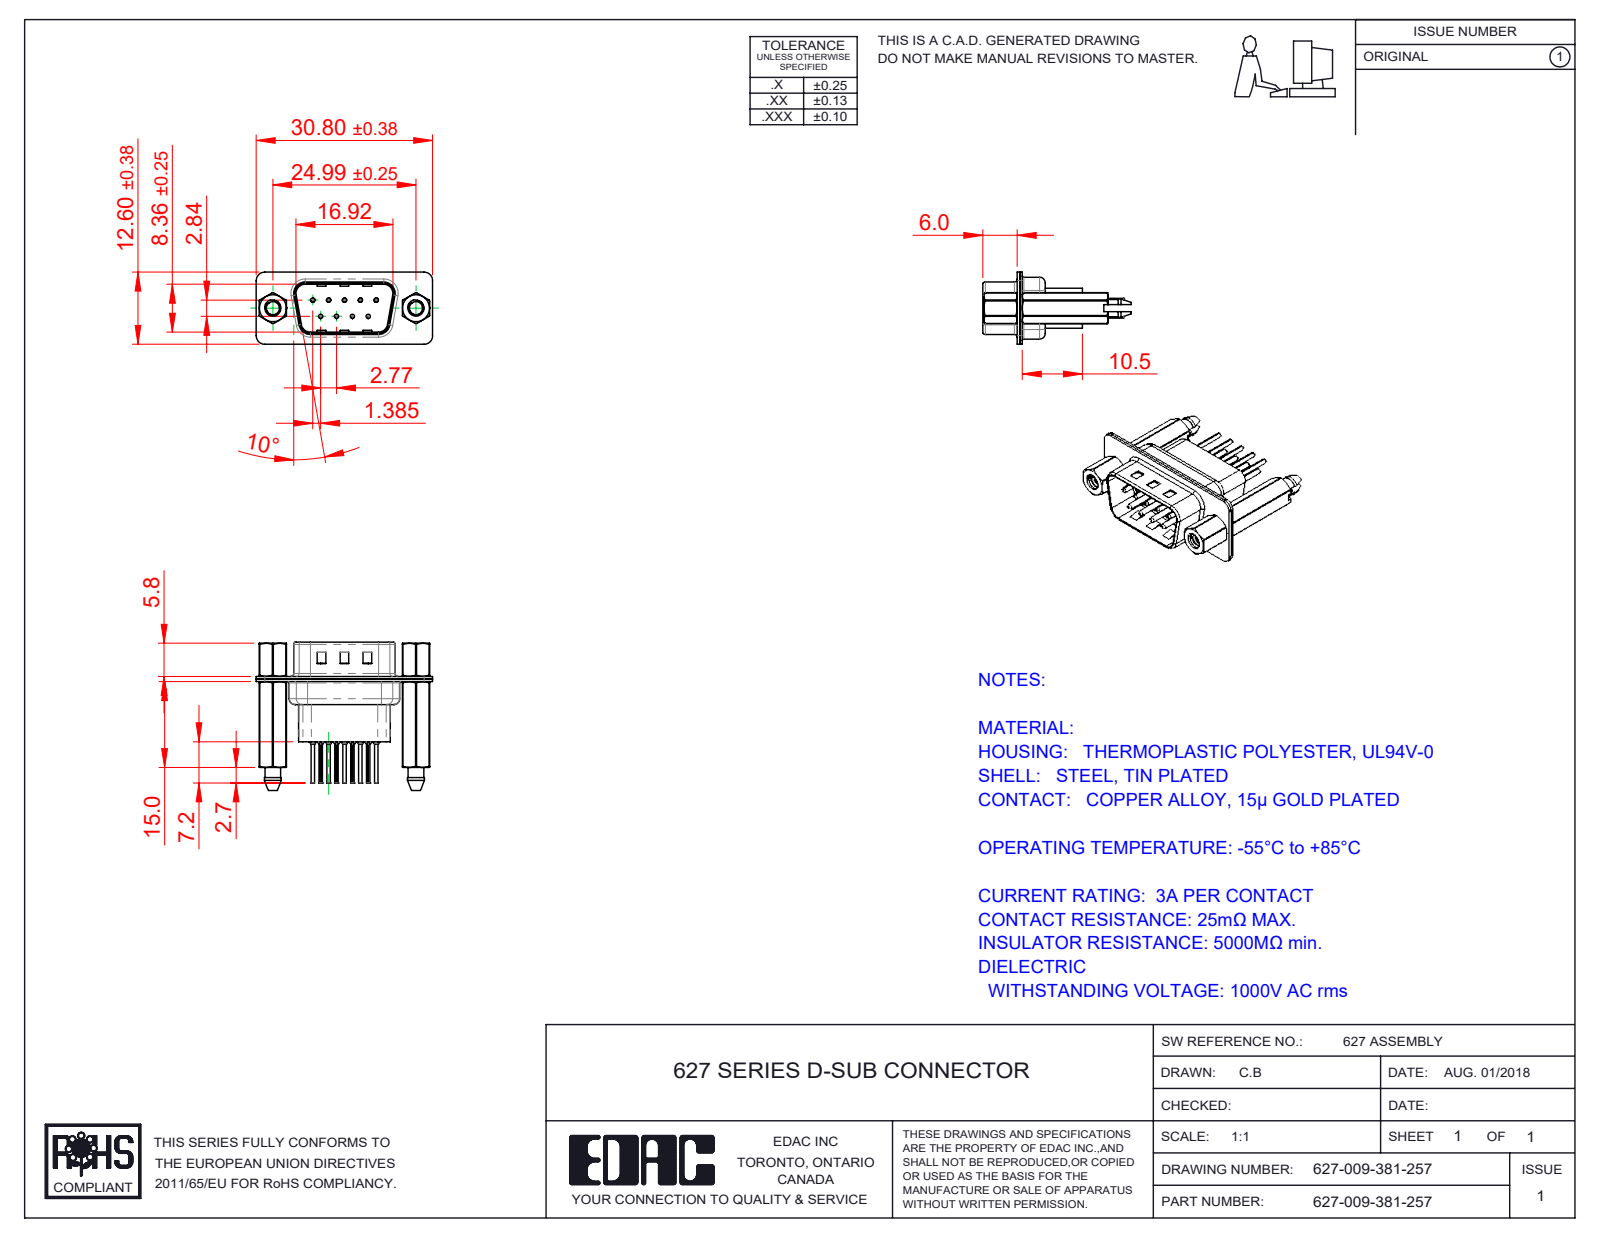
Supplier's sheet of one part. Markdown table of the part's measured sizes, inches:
| quantity | value |
| --- | --- |
| part name | 627 Shell Rear_09 Contacts; 627 Housing_09 HP; 627 Contact Row 1_61; 627 Shell Front_09 Contacts (+4 more) |
| STEP written by | SolidWorks 2020 (CONFIG_CONTROL_DESIGN) |
| units | inches |
| bodies | 16 solids, 1420 faces (377 planar, 600 cylindrical, 443 other) |
| overall size | 1.213 × 1.02 × 0.496 |
| volume | 0.145 in³ |
| surface area | 9.393 in² |
| round holes (diameter × count) | 0.008 × 9, 0.014 × 9, 0.043 × 9, 0.063 × 9, 0.089 × 2, 0.09 × 2, 0.157 × 2, 0.189 × 2 |
| round bosses / shafts (diameter × count) | 0.079 × 9, 0.059 × 9, 0.03 × 9, 0.024 × 9, 0.193 × 2, 0.11 × 2 |
| partial cylindrical surfaces (radius × count) | 0.059 × 20, 0.004 × 18, 0.079 × 12, 0.063 × 10, 0.02 × 8, 0.01 × 4, 0.024 × 4, 0.026 × 4 |
| main face-to-face distances | 0.018, 0.016, 0.035, 0.187, 0.032, 0.377, 0.055, 0.059, 0.027, 0.302 |
| hole center spacings | 0.124, 0.109, 0.218, 0.198, 0.198, 0.327, 0.294, 0.295 |
